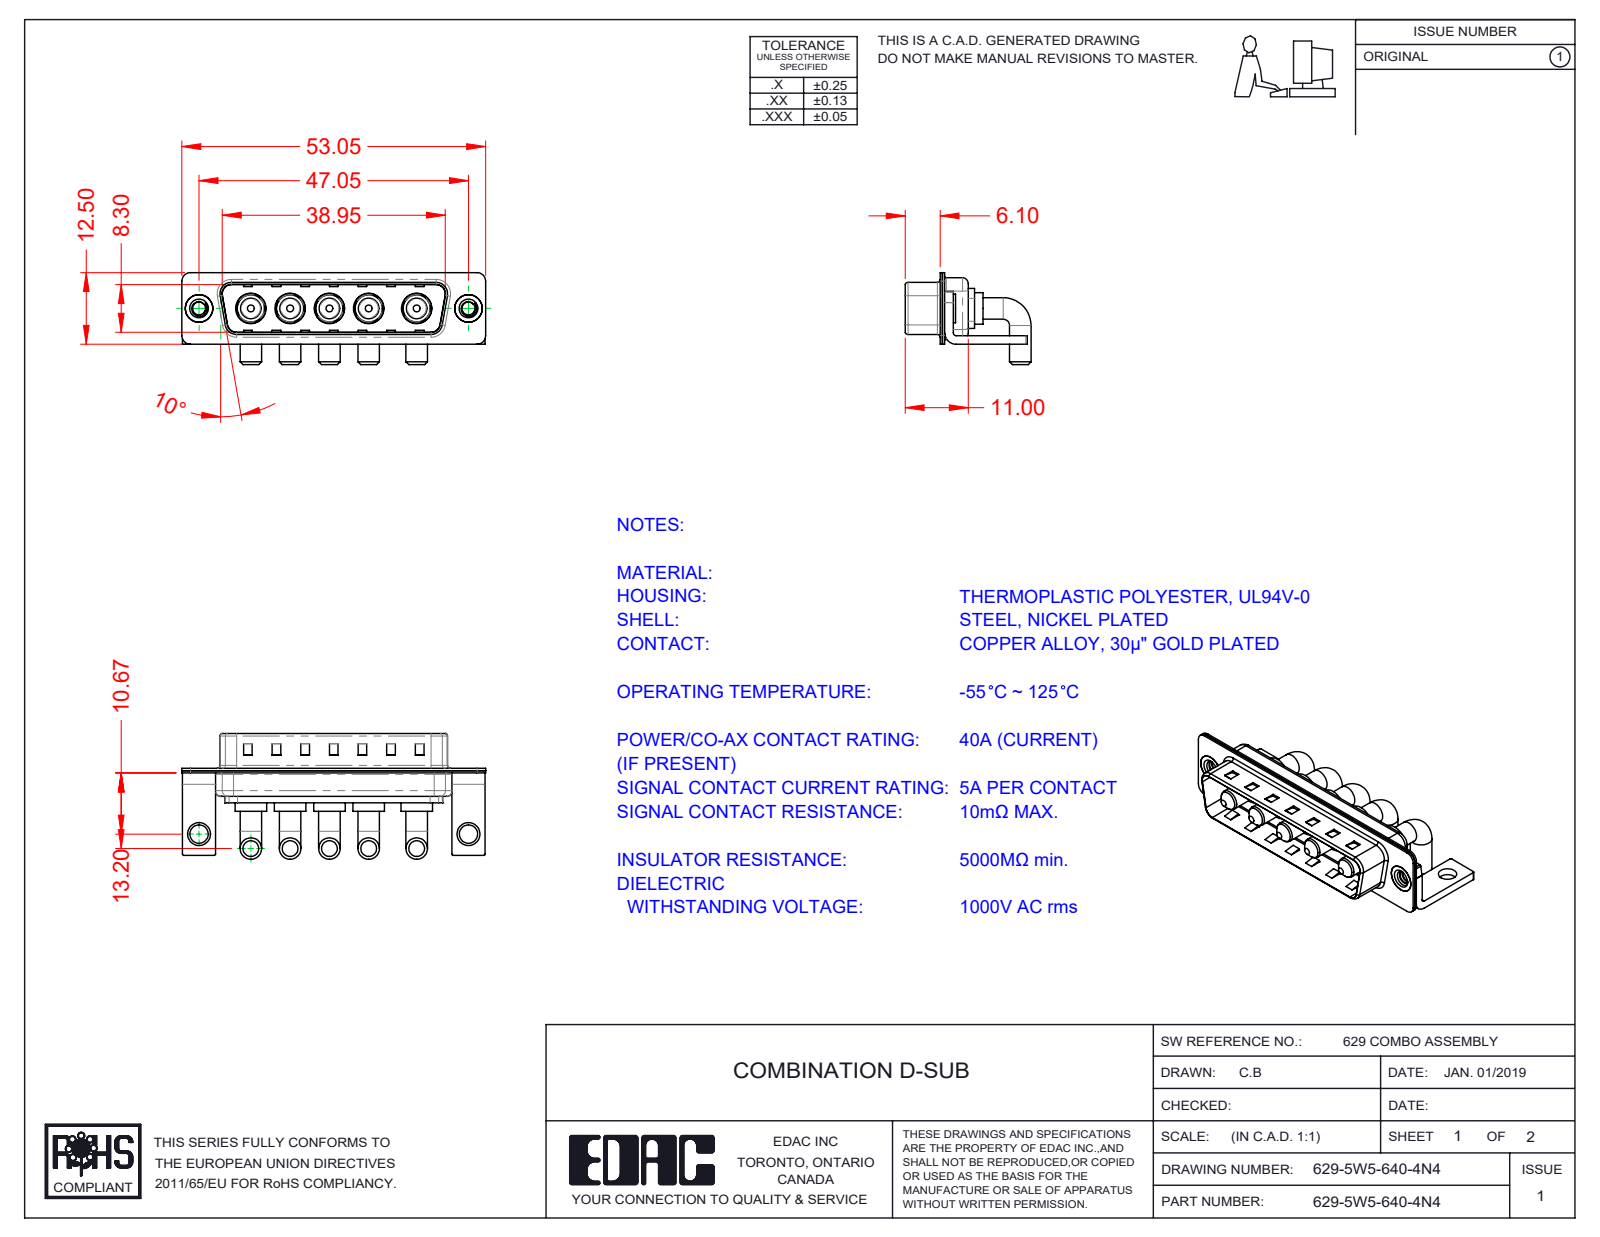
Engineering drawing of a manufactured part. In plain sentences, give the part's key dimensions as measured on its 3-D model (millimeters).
The part is named "629Combo Stabilizer Bracket; 629Combo Shell Front_25 Contacts; 629Combo Shell Rear_25 Contacts; Power Pin_40A RA (+3 more)". Its 3-D file was written by "SolidWorks 2020 (CONFIG_CONTROL_DESIGN)". It is 17 solids with 631 faces: 241 planar, 260 cylindrical and 130 other. Overall it measures 53.05 by 21.98 by 16.05 millimeters. Its volume is 4 034 cubic millimeters and its surface area 7 952 square millimeters. Round holes: 5 of diameter 4.85, 5 of diameter 5.3, 2 of diameter 2.26, 2 of diameter 3.2, 2 of diameter 4, 2 of diameter 4.8. Round bosses or shafts: 10 of diameter 3.75, 5 of diameter 5.5, 5 of diameter 5.2, 5 of diameter 4.75, 5 of diameter 3.6, 2 of diameter 5, 2 of diameter 4.9. Partial cylindrical surfaces (rounded edges, fillets, slot ends): 16 of radius 0.25, 16 of radius 1.5, 13 of radius 2, 9 of radius 0.5, 8 of radius 1.6, 5 of radius 2.1, 4 of radius 0.6, 4 of radius 0.65. The main face-to-face distances are 0.4, 0.8, 9.5, 1.5, 9.1, 8.7, 9.9, 5.2, 0.75, 1.2. The hole center spacings are 6.86, 13.73, 47.05, 6.85, 6.87, 8.37, 8.38, 9.04.
